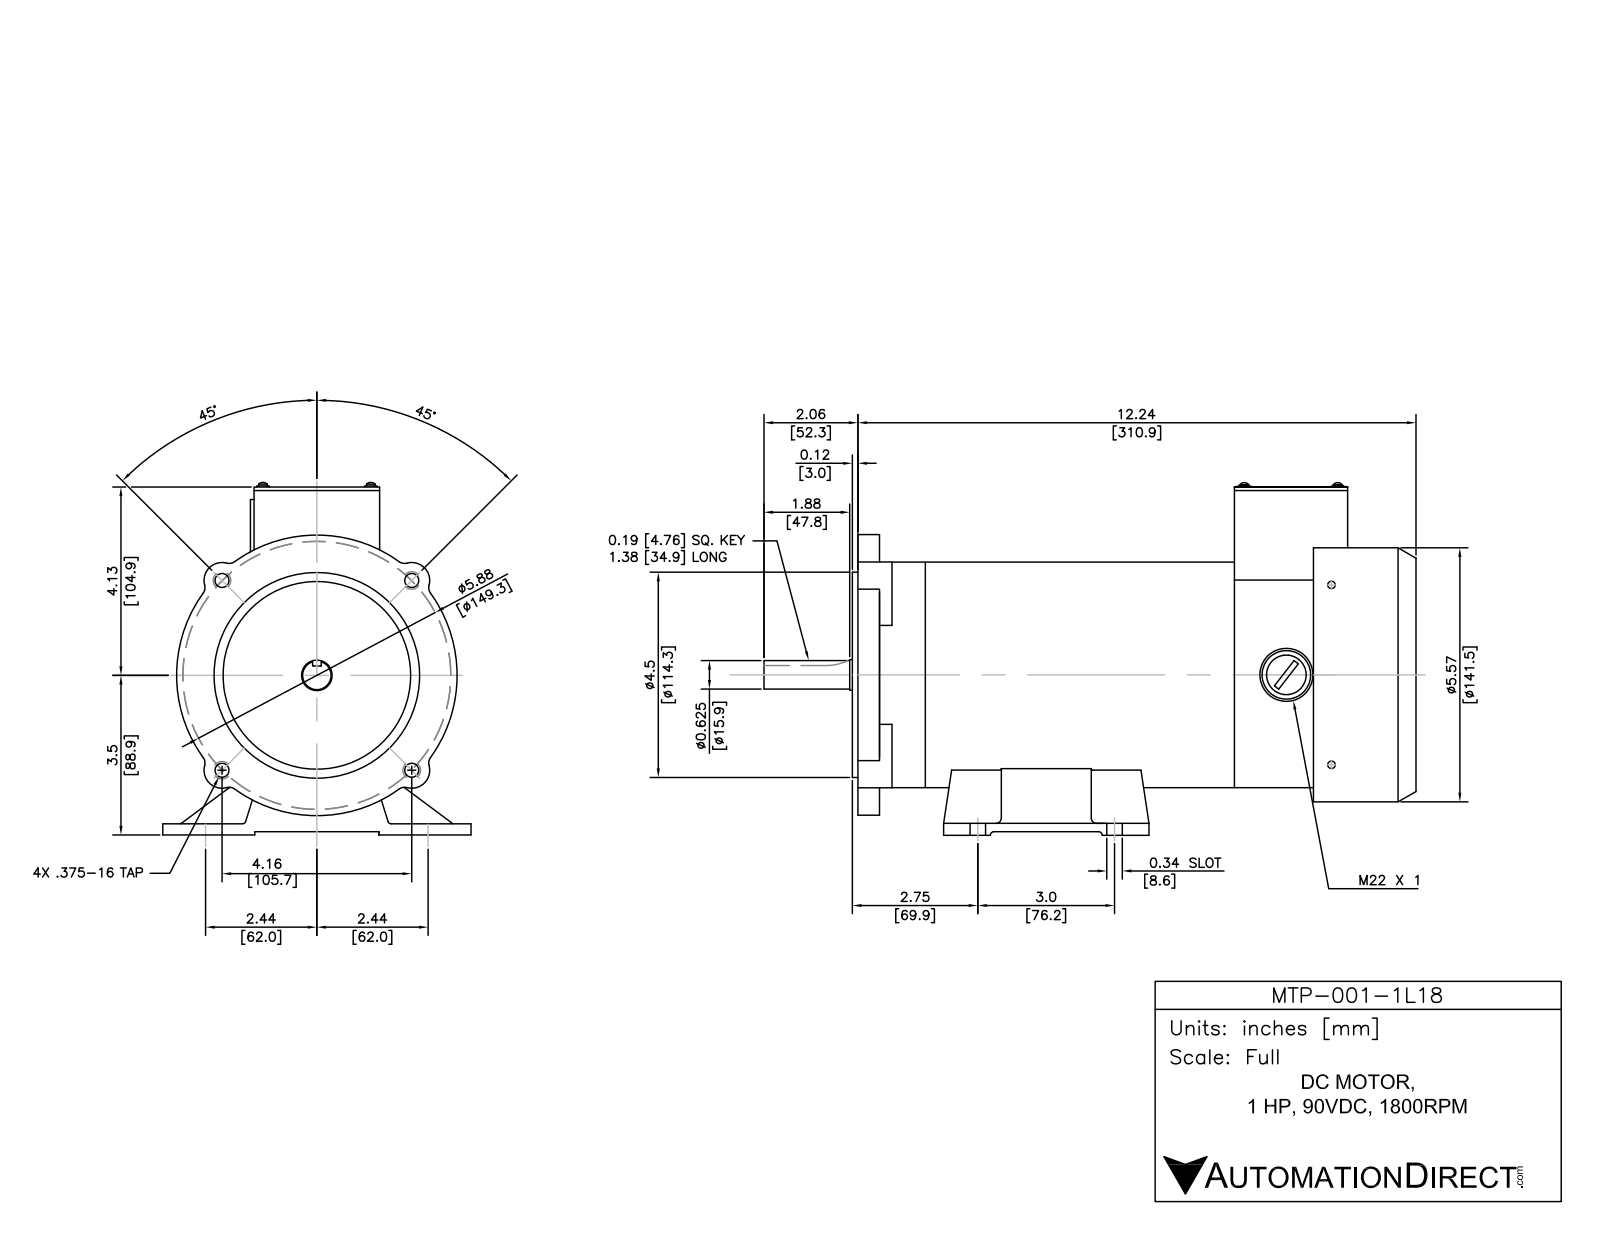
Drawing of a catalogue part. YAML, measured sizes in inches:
part_name: "WPMDC1-18-90-180-56CB b"
step_written_by: "SolidWorks 2017 (AUTOMOTIVE_DESIGN)"
units: inches
bodies: {solids: 33, faces: 1839, planar: 567, cylindrical: 873, other: 399}
overall_size: [14.339, 7.521, 6.496]
volume: 73.76
surface_area: 829.5
round_holes:
  - {diameter: 0.13, count: 10}
  - {diameter: 0.197, count: 8}
  - {diameter: 0.067, count: 2}
  - {diameter: 0.169, count: 2}
  - {diameter: 0.205, count: 2}
  - {diameter: 0.236, count: 2}
  - {diameter: 0.276, count: 2}
  - {diameter: 0.299, count: 2}
  - {diameter: 0.374, count: 2}
  - {diameter: 0.394, count: 2}
  - {diameter: 0.701, count: 2}
  - {diameter: 0.728, count: 2}
round_bosses_or_shafts:
  - {diameter: 0.157, count: 10}
  - {diameter: 0.354, count: 8}
  - {diameter: 0.331, count: 8}
  - {diameter: 1.063, count: 2}
  - {diameter: 0.39, count: 2}
  - {diameter: 6.142, count: 1}
  - {diameter: 5.575, count: 1}
  - {diameter: 5.512, count: 1}
partial_cylinders:
  - {radius: 0.02, count: 70}
  - {radius: 0.197, count: 38}
  - {radius: 0.039, count: 28}
  - {radius: 0.098, count: 18}
  - {radius: 0.236, count: 10}
  - {radius: 0.394, count: 9}
  - {radius: 0.118, count: 8}
  - {radius: 0.157, count: 8}
face_to_face_distances: [0.098, 0.079, 0.157, 0.059, 10.803, 1.535, 10.744, 0.031, 10.646, 12.28]
hole_center_spacings: [1.187, 2.166, 2.262, 2.362, 2.749, 0.103, 0.358, 0.937]
